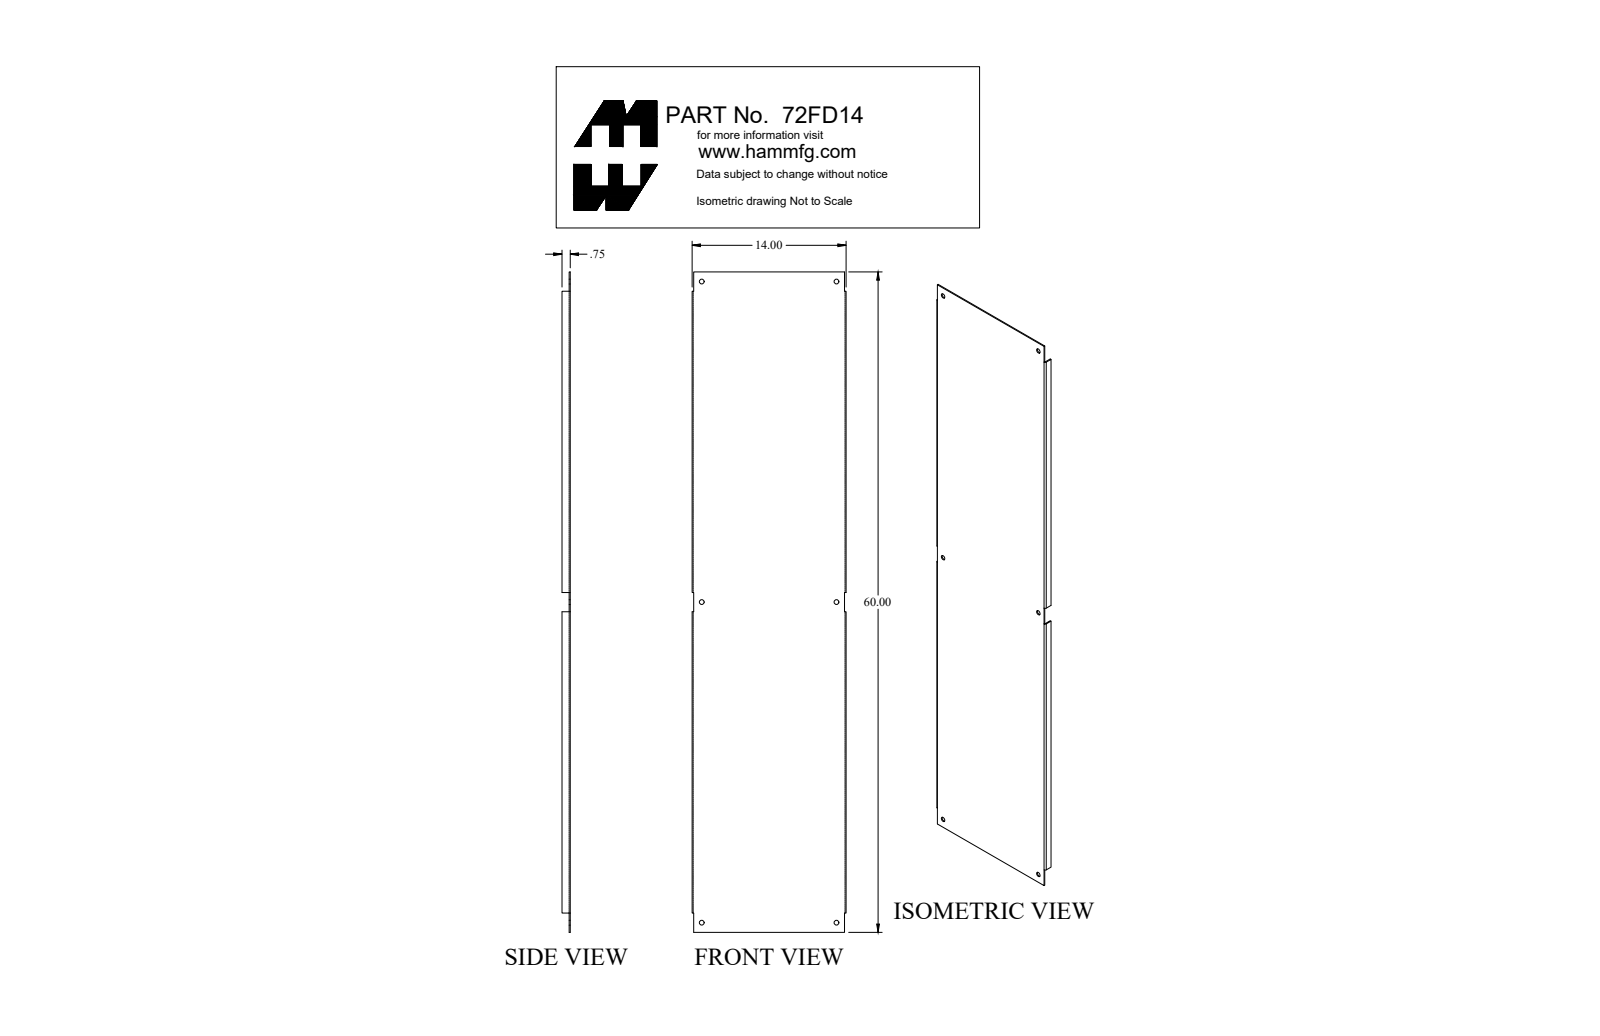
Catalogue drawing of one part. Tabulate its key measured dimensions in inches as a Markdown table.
| quantity | value |
| --- | --- |
| part name | 72FD14_Default |
| STEP written by | SolidWorks 2018 (CONFIG_CONTROL_DESIGN) |
| units | inches |
| bodies | 1 solid, 50 faces (30 planar, 20 cylindrical, 0 other) |
| overall size | 60 × 14 × 0.75 |
| volume | 85.96 in³ |
| surface area | 1 825 in² |
| round holes (diameter × count) | 0.437 × 6 |
| partial cylindrical surfaces (radius × count) | 0.048 × 2, 0.143 × 2 |
| main face-to-face distances | 0.095, 13.905, 14, 13.81, 0.75, 0.655, 60, 0.143, 13.857, 0.048 |
| hole center spacings | 29.125, 31.596, 12.25, 58.25, 59.524 |
